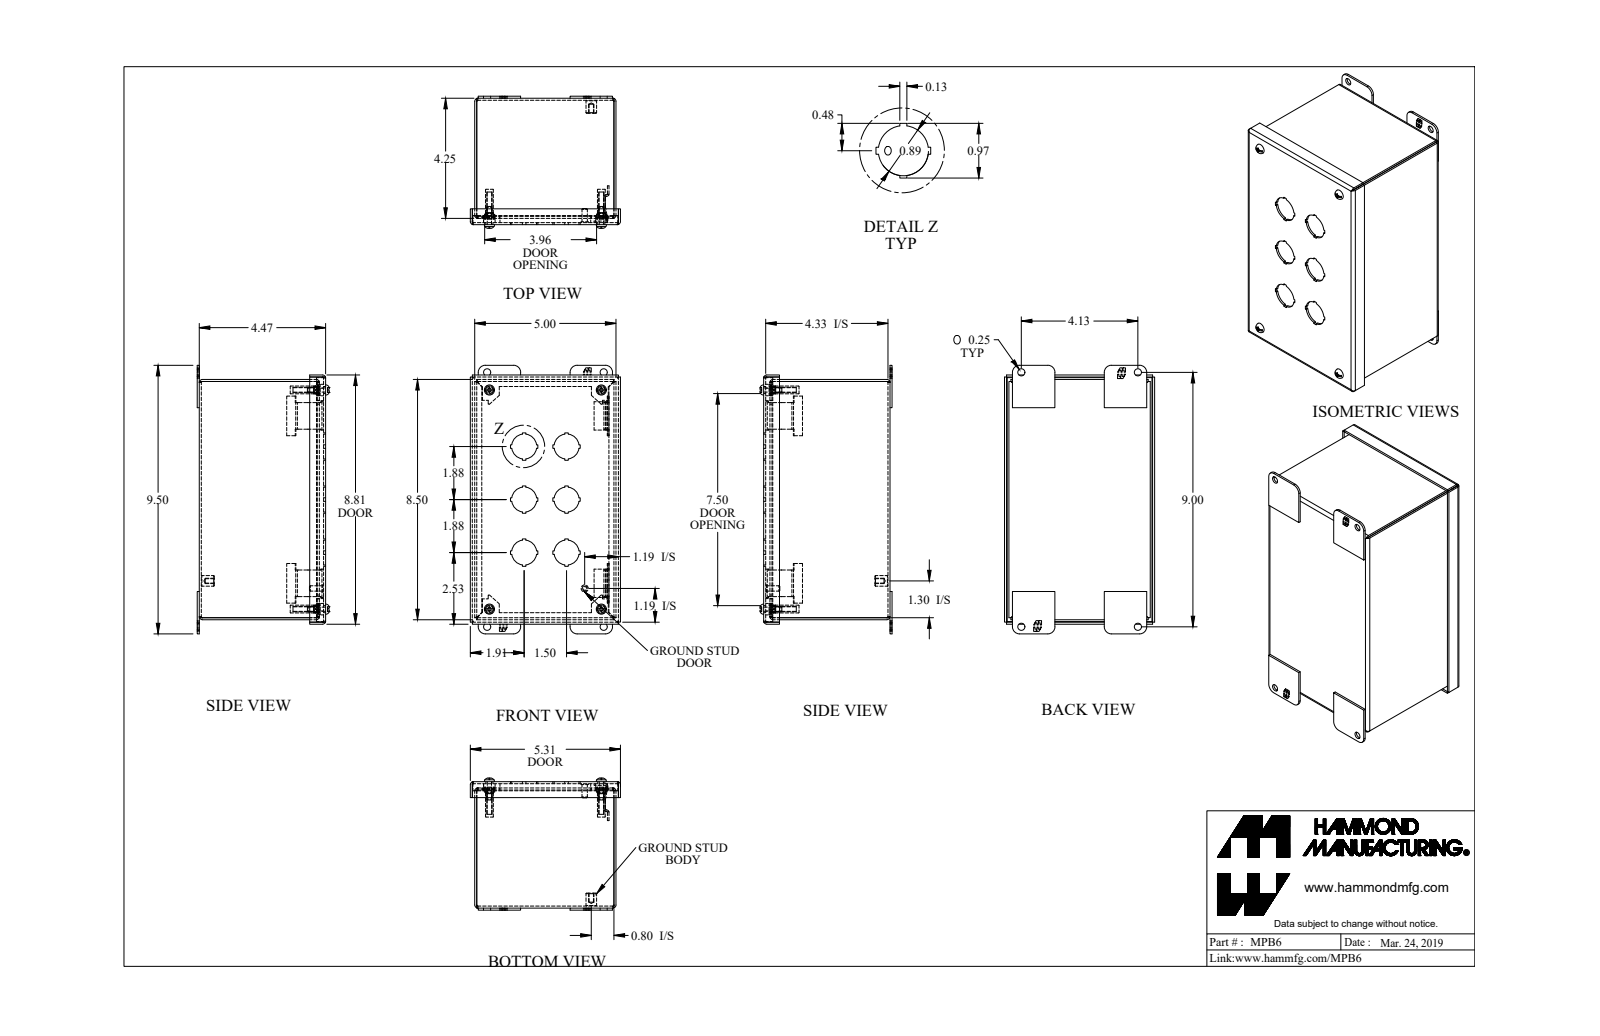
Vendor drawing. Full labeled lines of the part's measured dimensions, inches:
Part name (STEP PRODUCT): MPB6
STEP written by: SolidWorks 2018 (AUTOMOTIVE_DESIGN)
Units: inches
Bodies: 23 solids, 811 faces (571 planar, 184 cylindrical, 56 other)
Overall size (bounding box): 9.5 × 5.313 × 4.671
Volume: 18.99 in³ · Surface area: 506.7 in²
Round holes (diameter × count): ⌀0.25 ×8, ⌀0.886 ×6, ⌀0.159 ×4, ⌀0.406 ×4, ⌀0.156 ×1
Round bosses / shafts (diameter × count): ⌀0.39 ×4, ⌀0.275 ×4, ⌀0.19 ×4, ⌀0.148 ×4, ⌀0.375 ×1, ⌀0.25 ×1, ⌀0.188 ×1
Partial cylindrical surfaces — rounded edges, fillets, slot ends (radius × count): R0.036 ×12, R0.108 ×12, R0.25 ×8, R0.029 ×4, R0.086 ×4, R0.16 ×4, R0.171 ×4
Main face-to-face distances: 0.072, 4.4, 4.928, 4.472, 4.328, 8.428, 5, 4.856, 8.356, 8.5
Hole centre spacings: 3.961, 4.091, 0.63, 0.631, 2.401, 3.959, 3.962, 4.067
